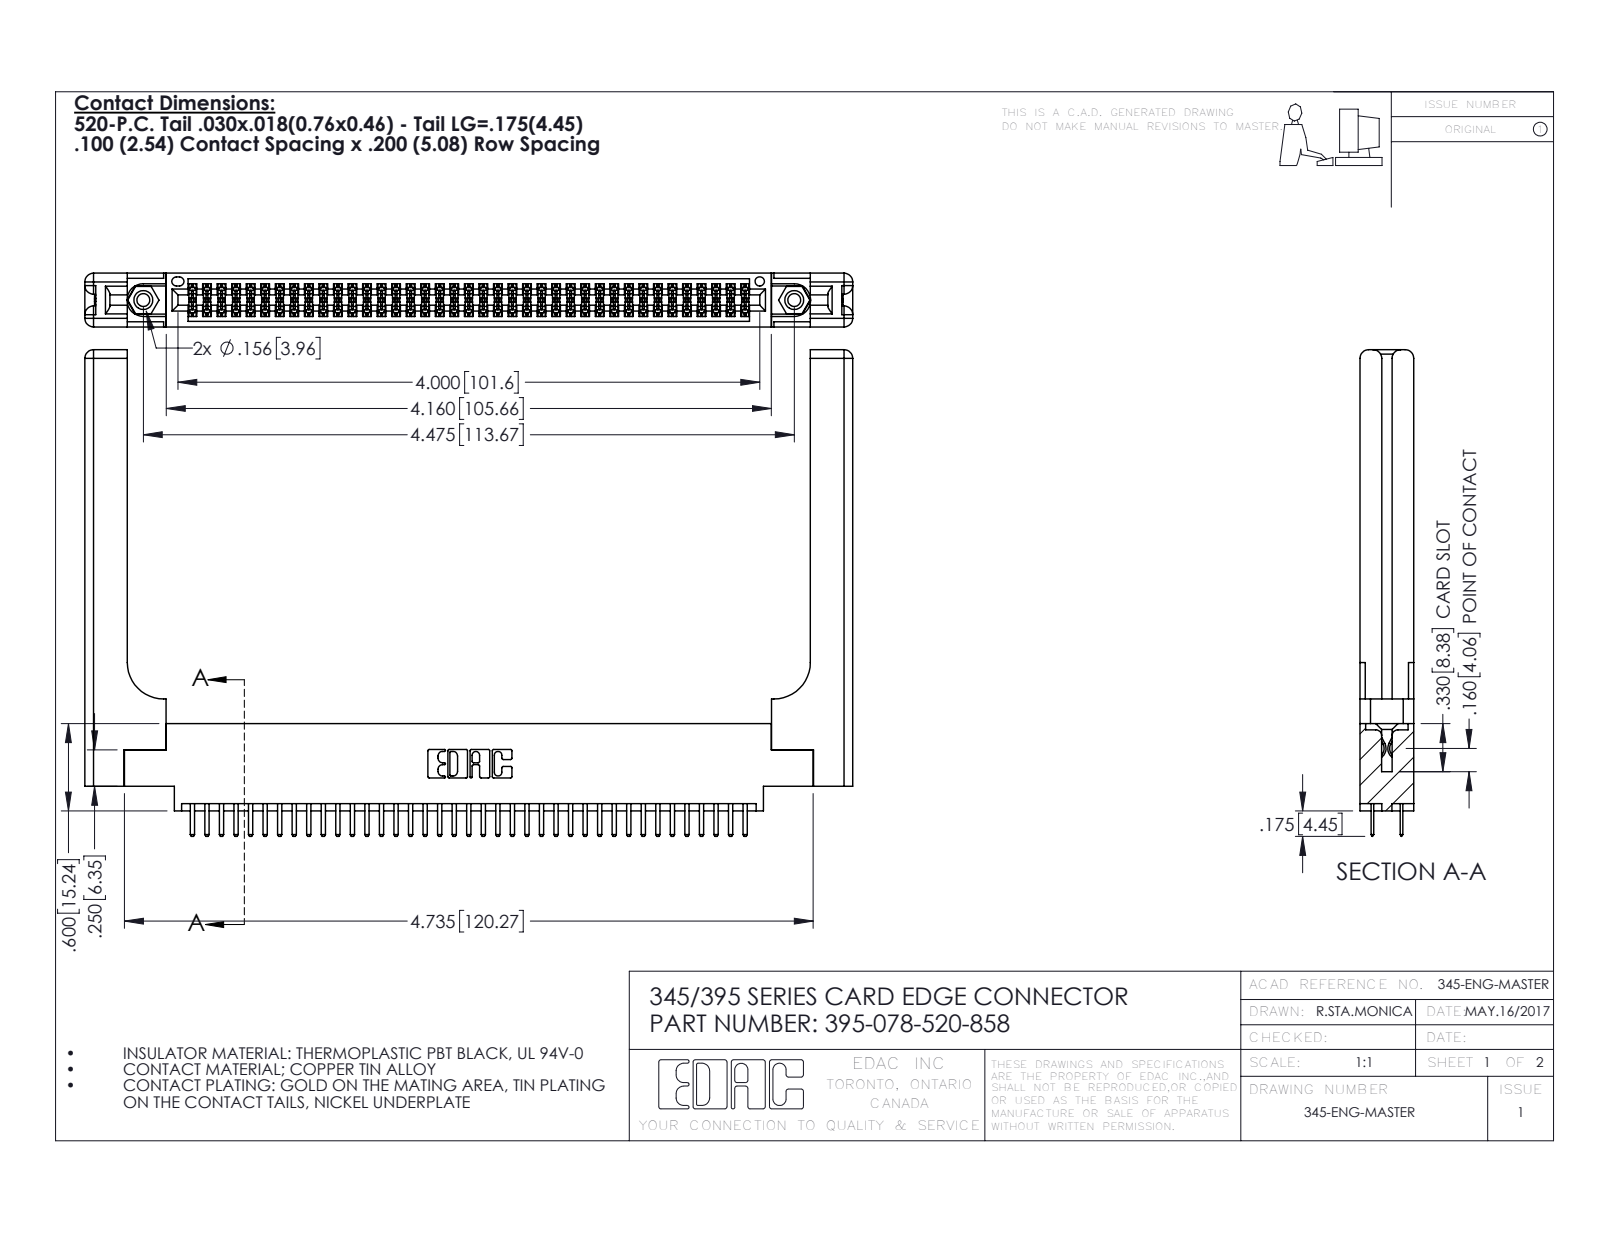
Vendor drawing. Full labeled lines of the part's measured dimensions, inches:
Part name (STEP PRODUCT): 345-220-058_345-220-058; 395-078-520-858; 345-250-001_345-250-001-102; 345-292-001_345-293-120 (+1 more)
STEP written by: SolidWorks 2016 (CONFIG_CONTROL_DESIGN)
Units: inches
Bodies: 83 solids, 4598 faces (2962 planar, 1576 cylindrical, 60 other)
Overall size (bounding box): 5.279 × 3.345 × 0.37
Volume: 1.301 in³ · Surface area: 37.3 in²
Round holes (diameter × count): ⌀0.089 ×2, ⌀0.125 ×2, ⌀0.156 ×2, ⌀0.064 ×1
Round bosses / shafts (diameter × count): ⌀0.155 ×2
Partial cylindrical surfaces — rounded edges, fillets, slot ends (radius × count): R0.006 ×117, R0.01 ×82, R0.01 ×22, R0.06 ×16, R0.007 ×6, R0.031 ×6, R0.026 ×3, R0.014 ×2
Main face-to-face distances: 0.37, 0.072, 0.298, 0.2, 0.098, 0.272, 0.025, 0.225, 0.148, 0.15
Hole centre spacings: 0.27, 4.239, 4.475
